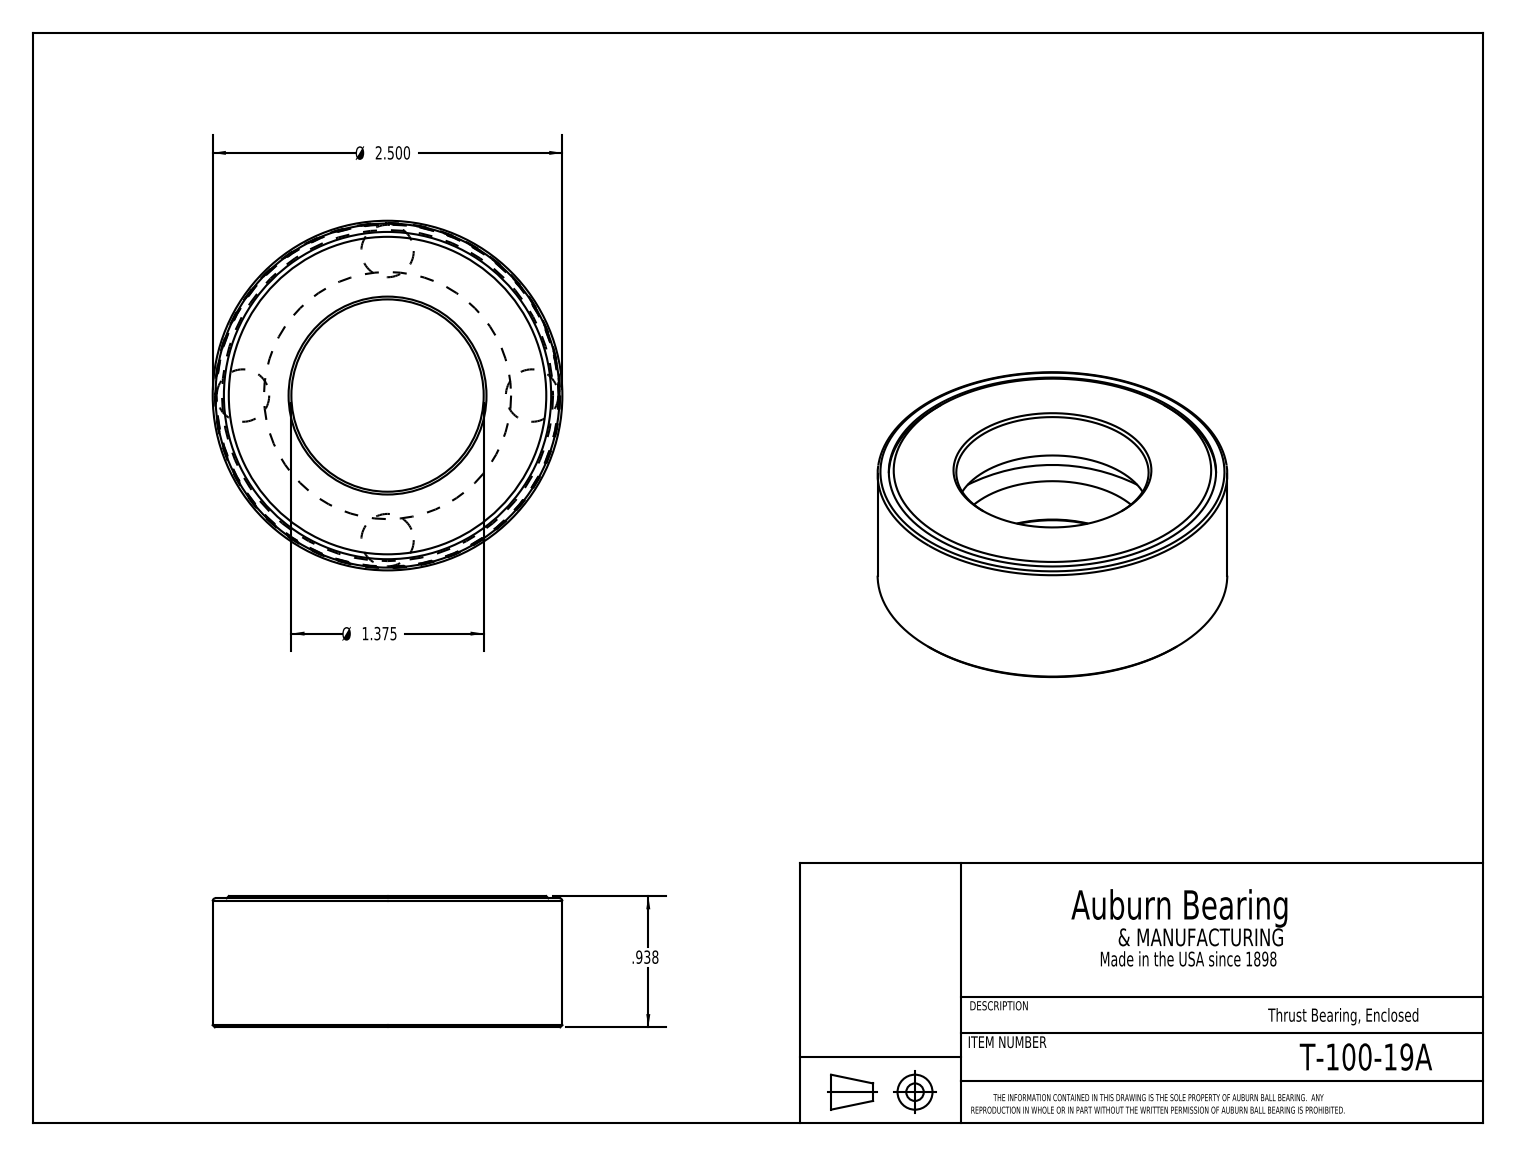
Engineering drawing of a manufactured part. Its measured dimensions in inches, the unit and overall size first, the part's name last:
Units: inches
Overall size (bounding box): 2.5 × 2.5 × 0.938
Round holes (diameter × count): ⌀1.375 ×1, ⌀1.375 ×1, ⌀2.34 ×1, ⌀2.46 ×1
Round bosses / shafts (diameter × count): ⌀2.5 ×1, ⌀2.446 ×1
Main face-to-face distances: 0.356, 0.581, 0.937, 0.225, 0.922, 0.566, 0.341, 0.015, 0.902, 0.546
Volume: 2.336 in³ · Surface area: 33.41 in²
Bodies: 6 solids, 28 faces (9 planar, 7 cylindrical, 12 other)
Part name (STEP PRODUCT): T-100-19A
STEP written by: SolidWorks 2016 (CONFIG_CONTROL_DESIGN)
